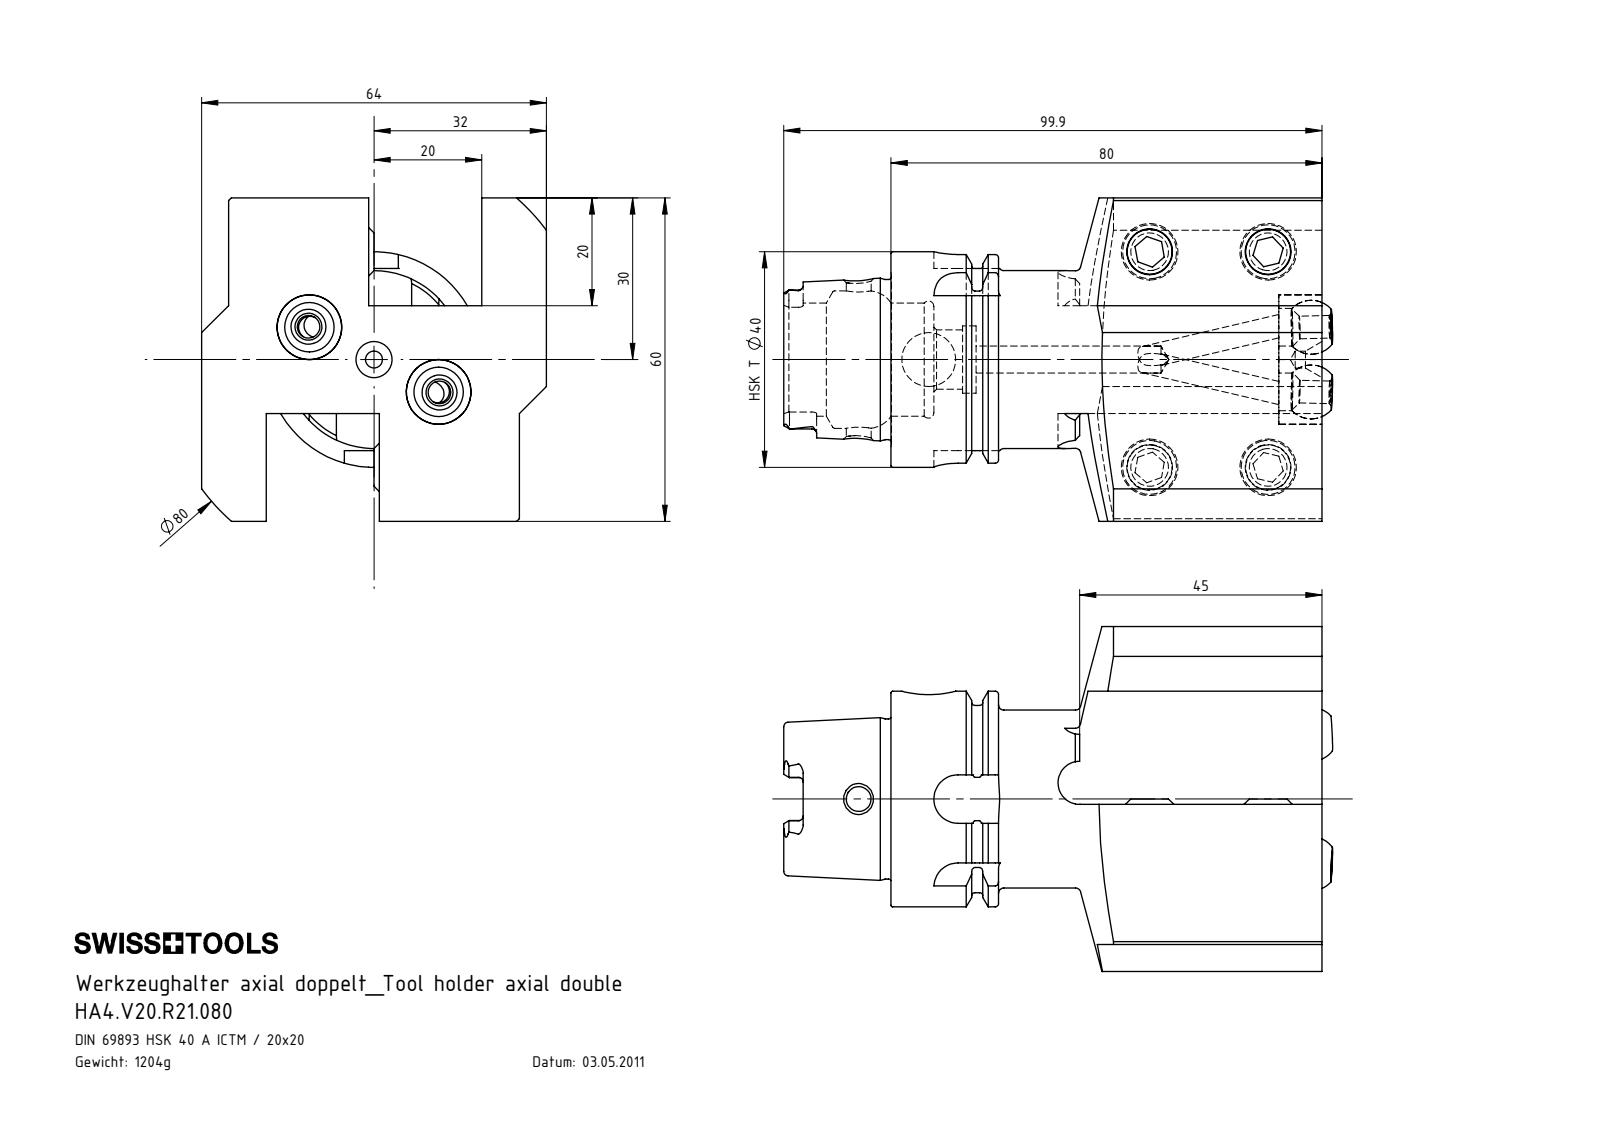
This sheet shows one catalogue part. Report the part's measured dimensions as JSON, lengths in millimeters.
{"part_name": "KU1-U12.001.010_2; KU1-U12.001.010_1; HA4-V20.R21.080_A_Fertigbearbeitung; ISO 4026 - M10 x 25 (+2 more)", "step_written_by": "SolidWorks 2017 (AUTOMOTIVE_DESIGN)", "units": "millimeters", "bodies": {"solids": 9, "faces": 318, "planar": 108, "cylindrical": 95, "other": 115}, "overall_size": [101.7, 64, 60], "volume_mm3": 153847, "surface_area_mm2": 38350, "round_holes": [[4.2, 4], [8.5, 4], [7, 2], [12, 2], [3.15, 1], [4.6, 1], [5, 1], [10, 1], [11, 1], [12.5, 1], [21, 1], [25.5, 1]], "round_bosses_or_shafts": [[10, 4], [40, 1], [34.75, 1], [33, 1], [29.71, 1]], "partial_cylinders_radius": [[4.5, 8], [0.9, 6], [1.88, 4], [0.5, 2], [40, 1]], "face_to_face_distances": [20, 40, 12, 52, 5, 19, 7, 26, 31, 33], "hole_center_spacings": [13.42, 22, 40, 45.62, 45.65, 66.1, 26.83]}
